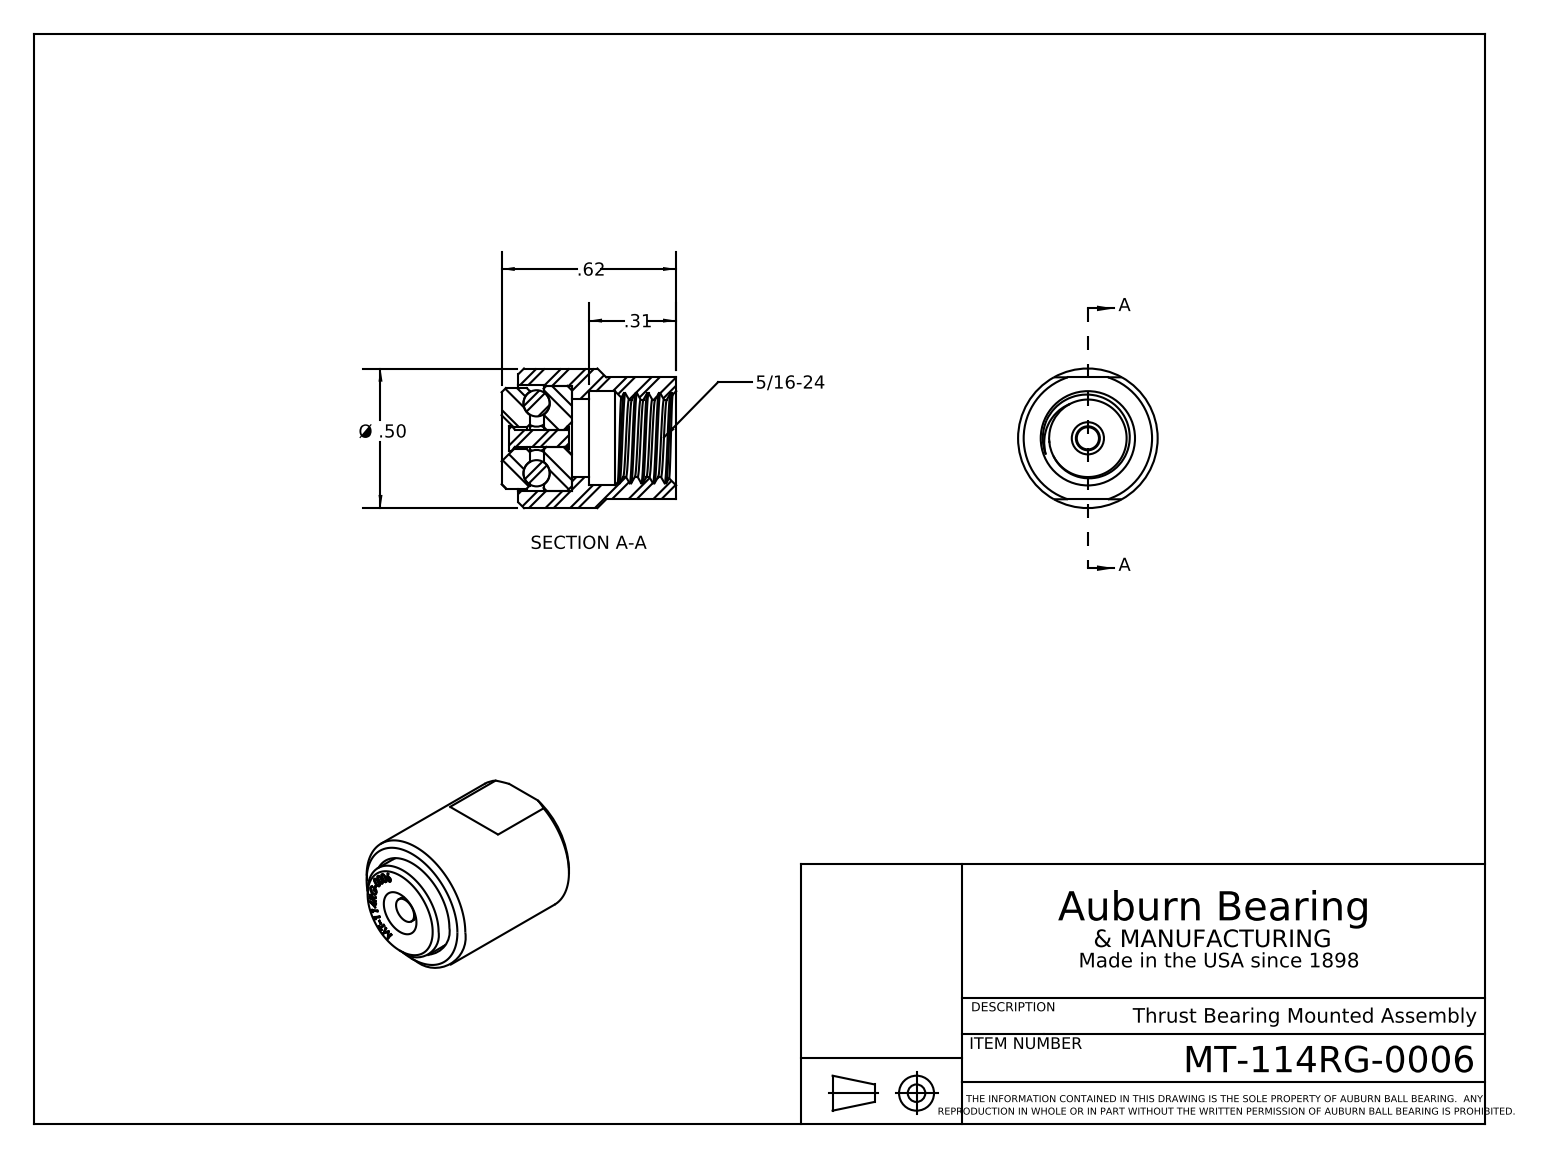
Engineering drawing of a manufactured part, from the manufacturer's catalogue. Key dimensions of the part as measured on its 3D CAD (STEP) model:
Part name (STEP PRODUCT): MT-114RG-0006
STEP written by: SolidWorks 2020 (CONFIG_CONTROL_DESIGN)
Units: inches
Bodies: 12 solids, 243 faces (109 planar, 31 cylindrical, 103 other)
Overall size (bounding box): 0.624 × 0.499 × 0.499
Volume: 0.08 in³ · Surface area: 2.759 in²
Round holes (diameter × count): ⌀0.062 ×1, ⌀0.078 ×1, ⌀0.277 ×1, ⌀0.28 ×1, ⌀0.335 ×1, ⌀0.374 ×1, ⌀0.378 ×1
Round bosses / shafts (diameter × count): ⌀0.499 ×1, ⌀0.375 ×1, ⌀0.359 ×1, ⌀0.091 ×1
Main face-to-face distances: 0.374, 0.25, 0.624, 0.436, 0.06, 0.19, 0.564, 0.1, 0.15, 0.09
